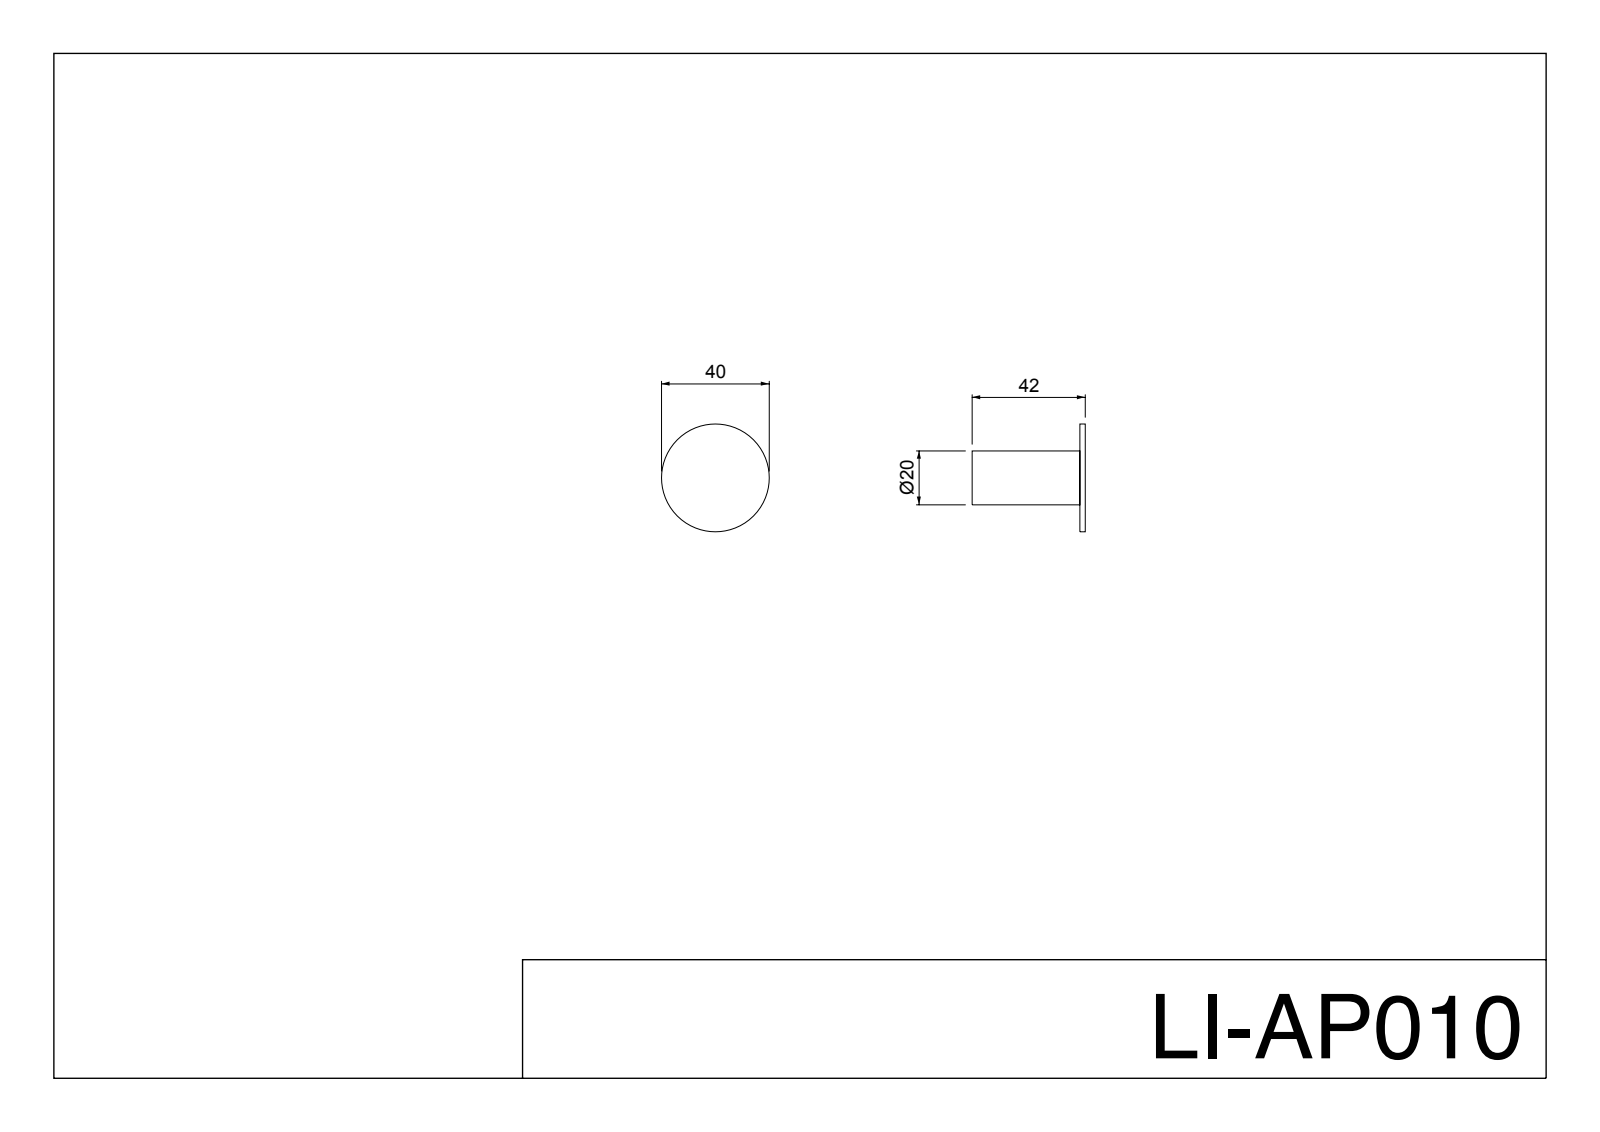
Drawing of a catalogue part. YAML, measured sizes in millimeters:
step_written_by: "ST-DEVELOPER v15 (AUTOMOTIVE_DESIGN)"
units: millimeters
bodies: {solids: 1, faces: 10, planar: 0, cylindrical: 0, other: 10}
overall_size: [42, 40, 40]
volume: 15117
surface_area: 5285
